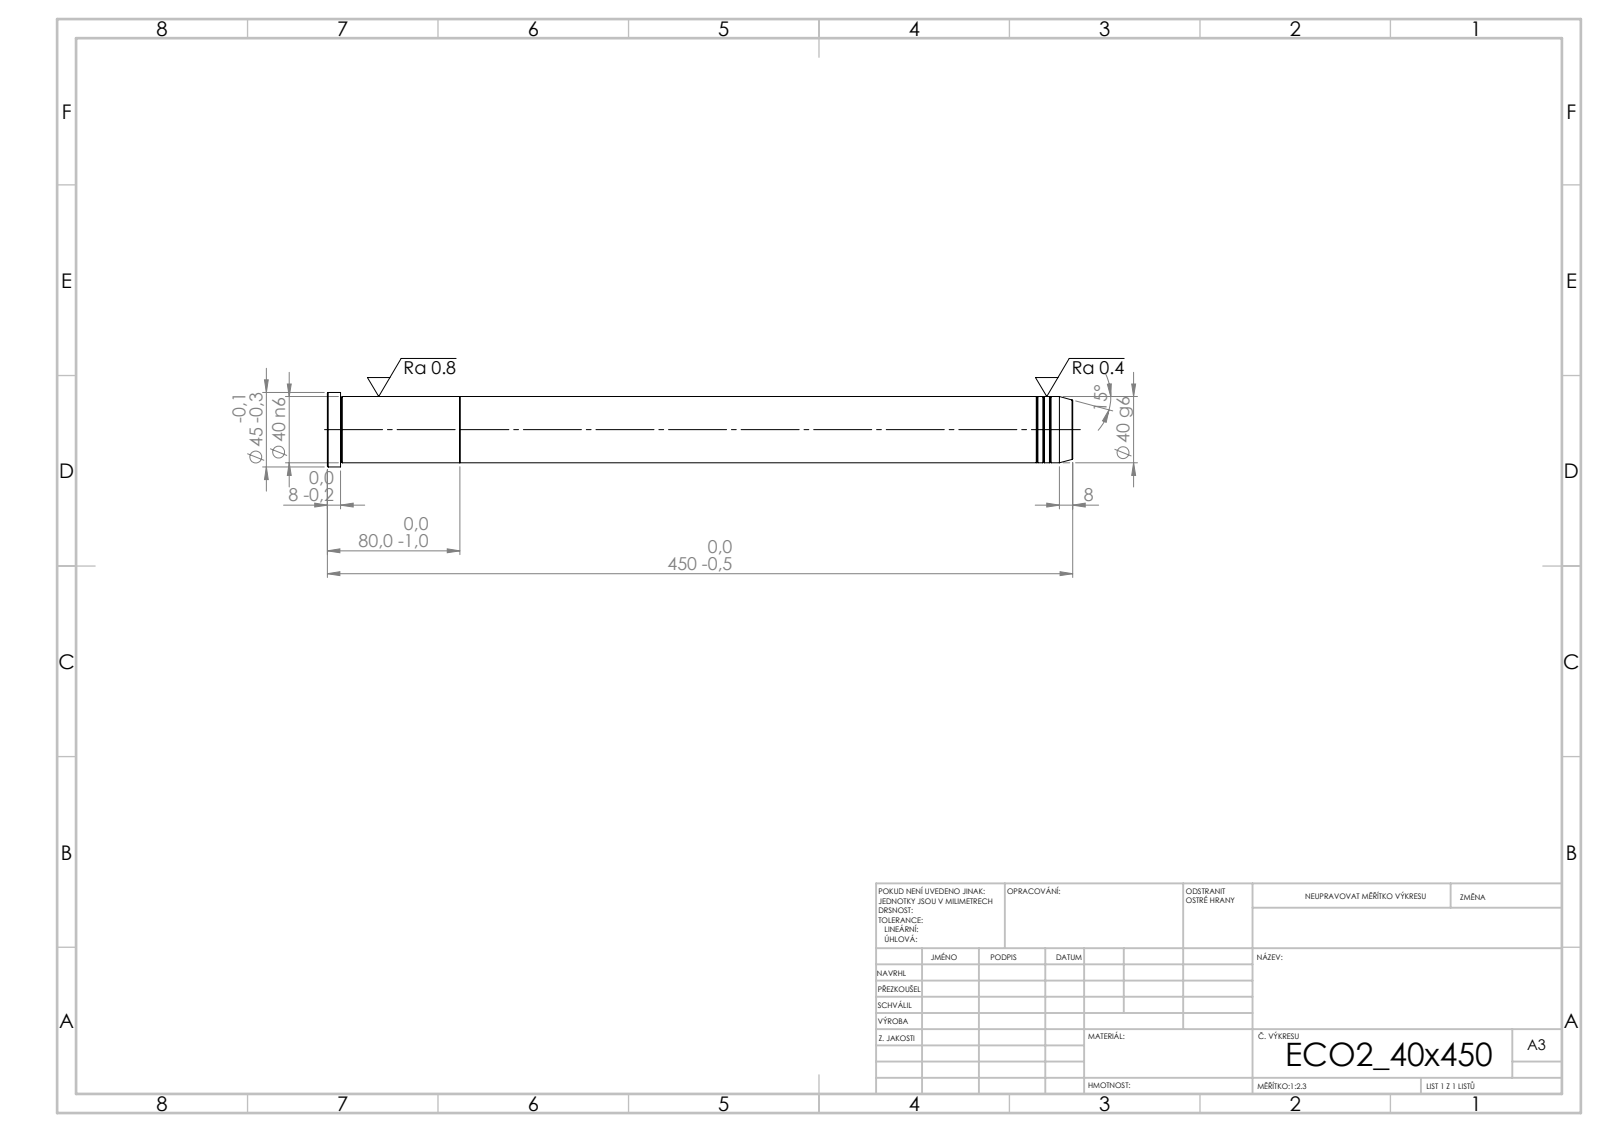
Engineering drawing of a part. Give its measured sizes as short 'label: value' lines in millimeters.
written by: SolidWorks 2019 (CONFIG_CONTROL_DESIGN)
unit: mm
bodies: 2 solids, 39 faces (5 planar, 12 cylindrical, 22 other)
size: 450 × 45 × 45
volume: 566 902 mm³; area: 62 313 mm²
bosses: 1× ⌀45, 1× ⌀40
face distances: 80, 370, 450, 442, 72, 8
